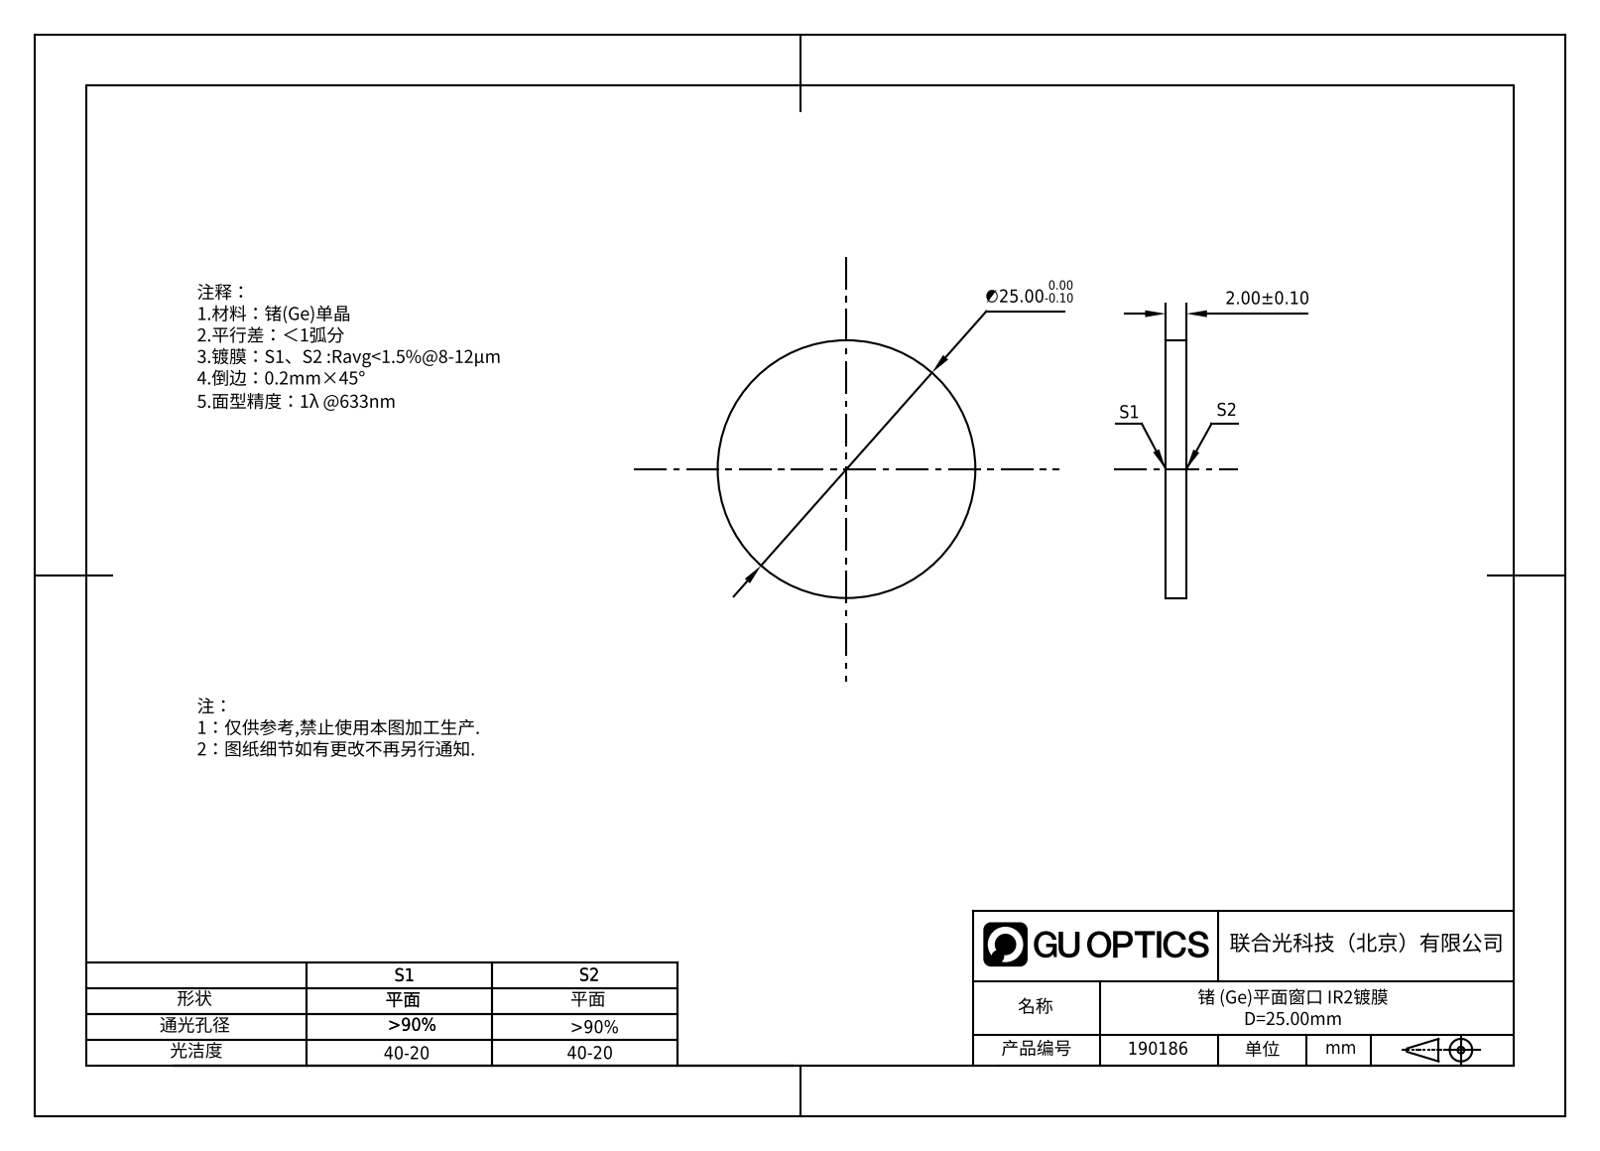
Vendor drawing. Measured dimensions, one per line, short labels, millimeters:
name: 190165
written by: SolidWorks 2016 (AUTOMOTIVE_DESIGN)
unit: mm
bodies: 1 solid, 4 faces (2 planar, 2 cylindrical, 0 other)
size: 25 × 25 × 2
volume: 982 mm³; area: 1 139 mm²
bosses: 1× ⌀25
face distances: 2
